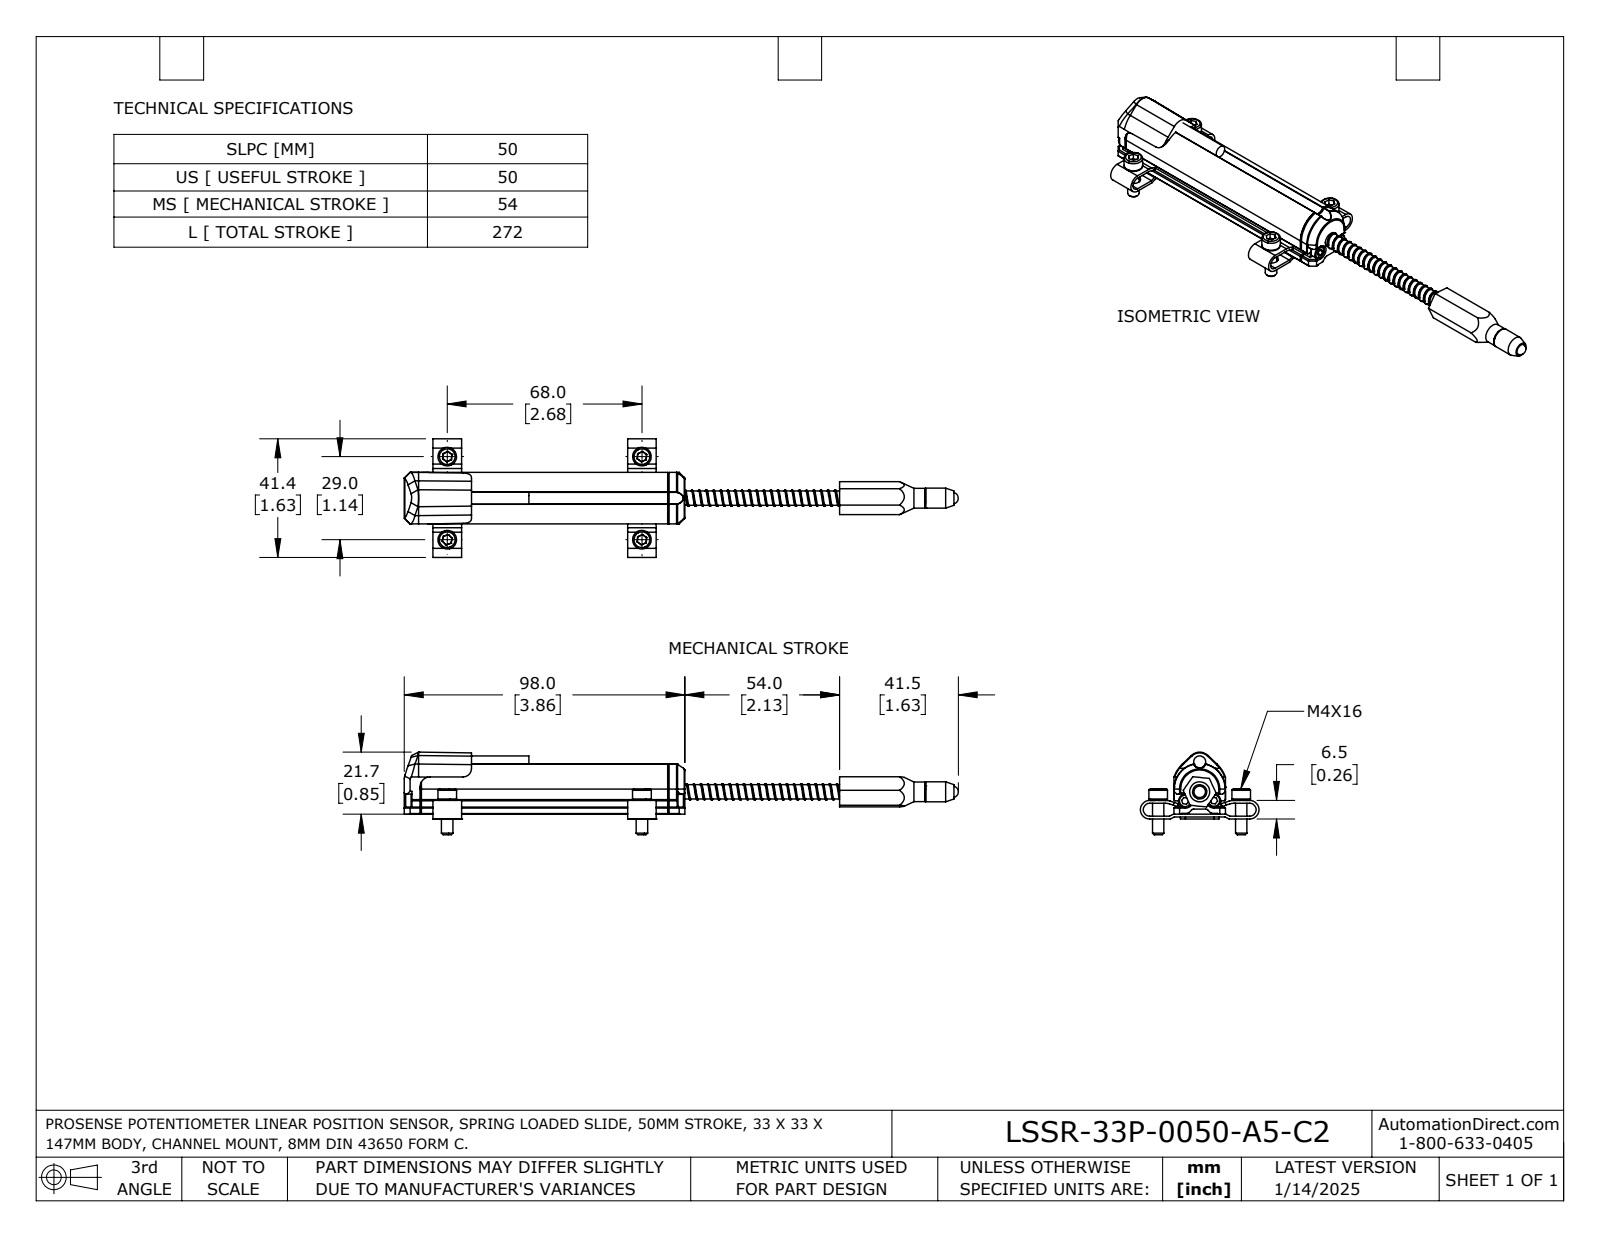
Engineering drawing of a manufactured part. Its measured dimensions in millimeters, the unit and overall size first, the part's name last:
Units: millimetres
Overall size (bounding box): 193.5 × 41.4 × 28.9
Round holes (diameter × count): ⌀4.5 ×4, ⌀5 ×4, ⌀2.6 ×2, ⌀2.6 ×2, ⌀4 ×1, ⌀5.4 ×1, ⌀6.9 ×1, ⌀6.9 ×1, ⌀8.5 ×1
Round bosses / shafts (diameter × count): ⌀6.5 ×4, ⌀4 ×4, ⌀4.6 ×3, ⌀2.9 ×2, ⌀1.5 ×2, ⌀7 ×1, ⌀5 ×1, ⌀4.2 ×1
Partial cylindrical surfaces — rounded edges, fillets, slot ends (radius × count): R0.2 ×8, R1.5 ×8, R0.1 ×6, R0.5 ×6, R0.3 ×4, R1.2 ×4, R1.8 ×4, R2.3 ×4
Main face-to-face distances: 1, 0.7, 0.5, 86.5, 10, 3.5, 18, 2.5, 86, 5.5
Hole centre spacings: 5.9, 29, 68, 73.9, 10
Volume: 33 510 mm³ · Surface area: 22 410 mm²
Bodies: 22 solids, 627 faces (376 planar, 184 cylindrical, 67 other)
Part name (STEP PRODUCT): LSSR-33P-0050-A5-C2
STEP written by: SolidWorks 2023 (AUTOMOTIVE_DESIGN)
